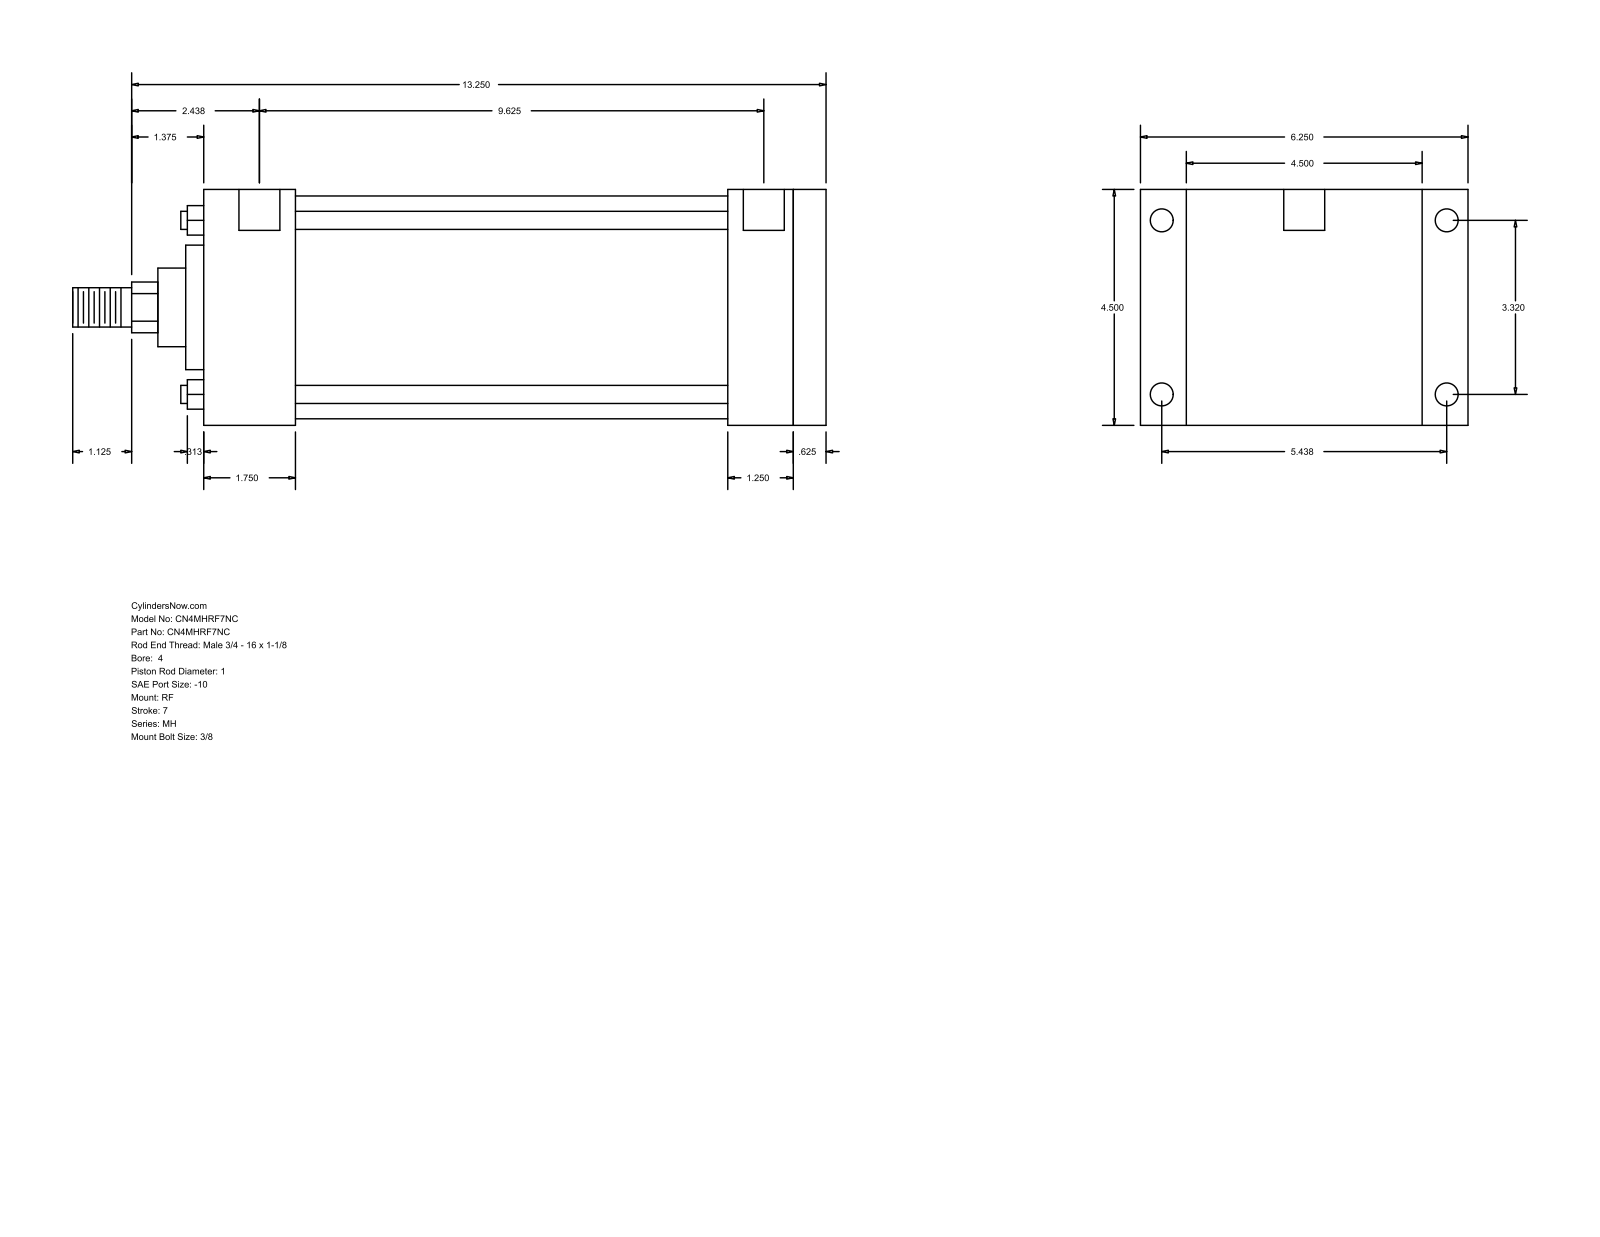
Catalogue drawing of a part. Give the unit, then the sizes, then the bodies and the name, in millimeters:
Units: millimetres
Overall size (bounding box): 365.12 × 158.75 × 114.3
Round holes (diameter × count): ⌀8.73 ×4, ⌀11.13 ×4, ⌀19.84 ×2
Round bosses / shafts (diameter × count): ⌀8.76 ×4, ⌀107.95 ×1, ⌀60.33 ×1, ⌀38.1 ×1, ⌀25.4 ×1, ⌀19.05 ×1
Partial cylindrical surfaces — rounded edges, fillets, slot ends (radius × count): R12.29 ×1
Main face-to-face distances: 114.3, 301.63, 285.76, 15.87, 44.46, 241.3, 257.17, 254.01, 209.55, 31.75
Hole centre spacings: 84.32, 138.12, 161.82, 247.65, 1.58, 1.59, 244.48, 246.06
Bodies: 0 solids, 94 faces (65 planar, 29 cylindrical, 0 other)
Part name (STEP PRODUCT): MH_RF__0400_1
STEP written by: GSSL Pune (CONFIG_CONTROL_DESIGN)
